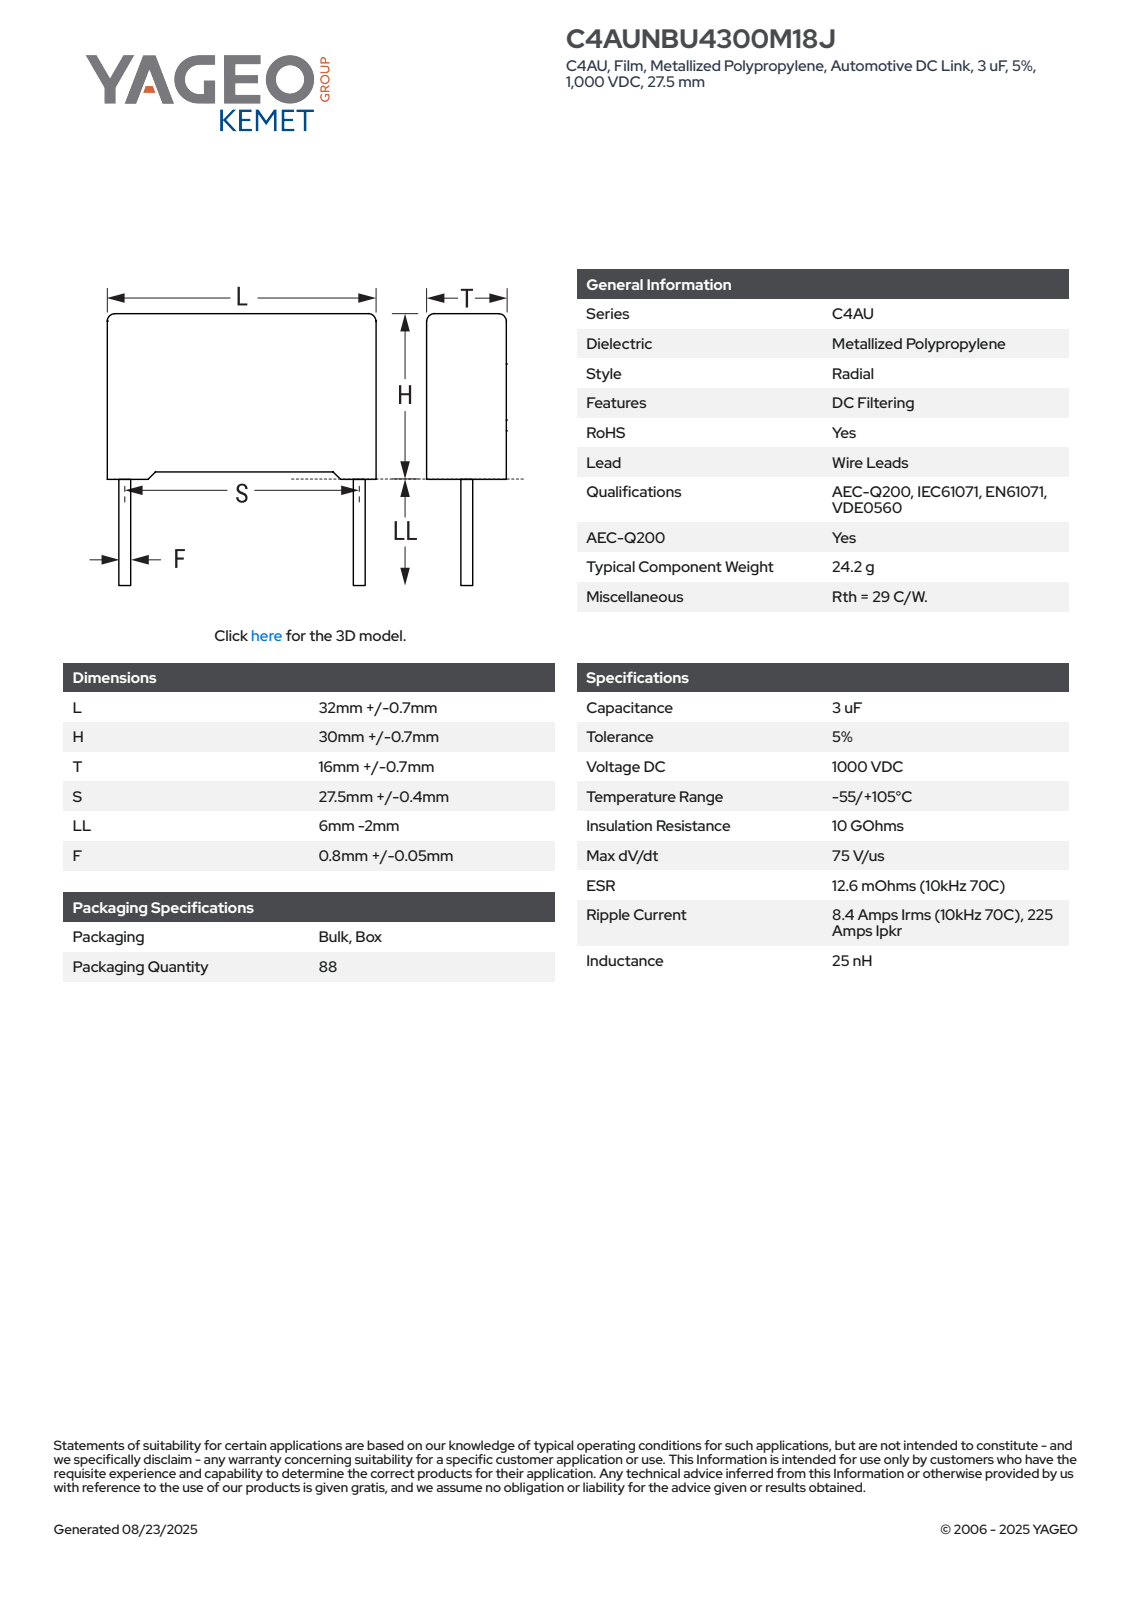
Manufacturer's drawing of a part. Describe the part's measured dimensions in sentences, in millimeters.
The part is named "CFR_RB2CFP_32X30X16_L32.7H30.7T16.7S27.5LL4F0.85". Its 3-D file was written by "SolidWorks 2014 (AUTOMOTIVE_DESIGN)". It is 4 solids with 85 faces: 77 planar, 8 cylindrical and 0 other. Overall it measures 34.7 by 32.7 by 16.7 millimeters. Its volume is 16 276 cubic millimeters and its surface area 4 198 square millimeters. Round bosses or shafts: 2 of diameter 0.85. Partial cylindrical surfaces (rounded edges, fillets, slot ends): 4 of radius 0.5. The main face-to-face distances are 16.7, 32.7, 29.64, 0.31, 29.95, 0.75, 1.06, 30.7, 1.09, 31.61.
